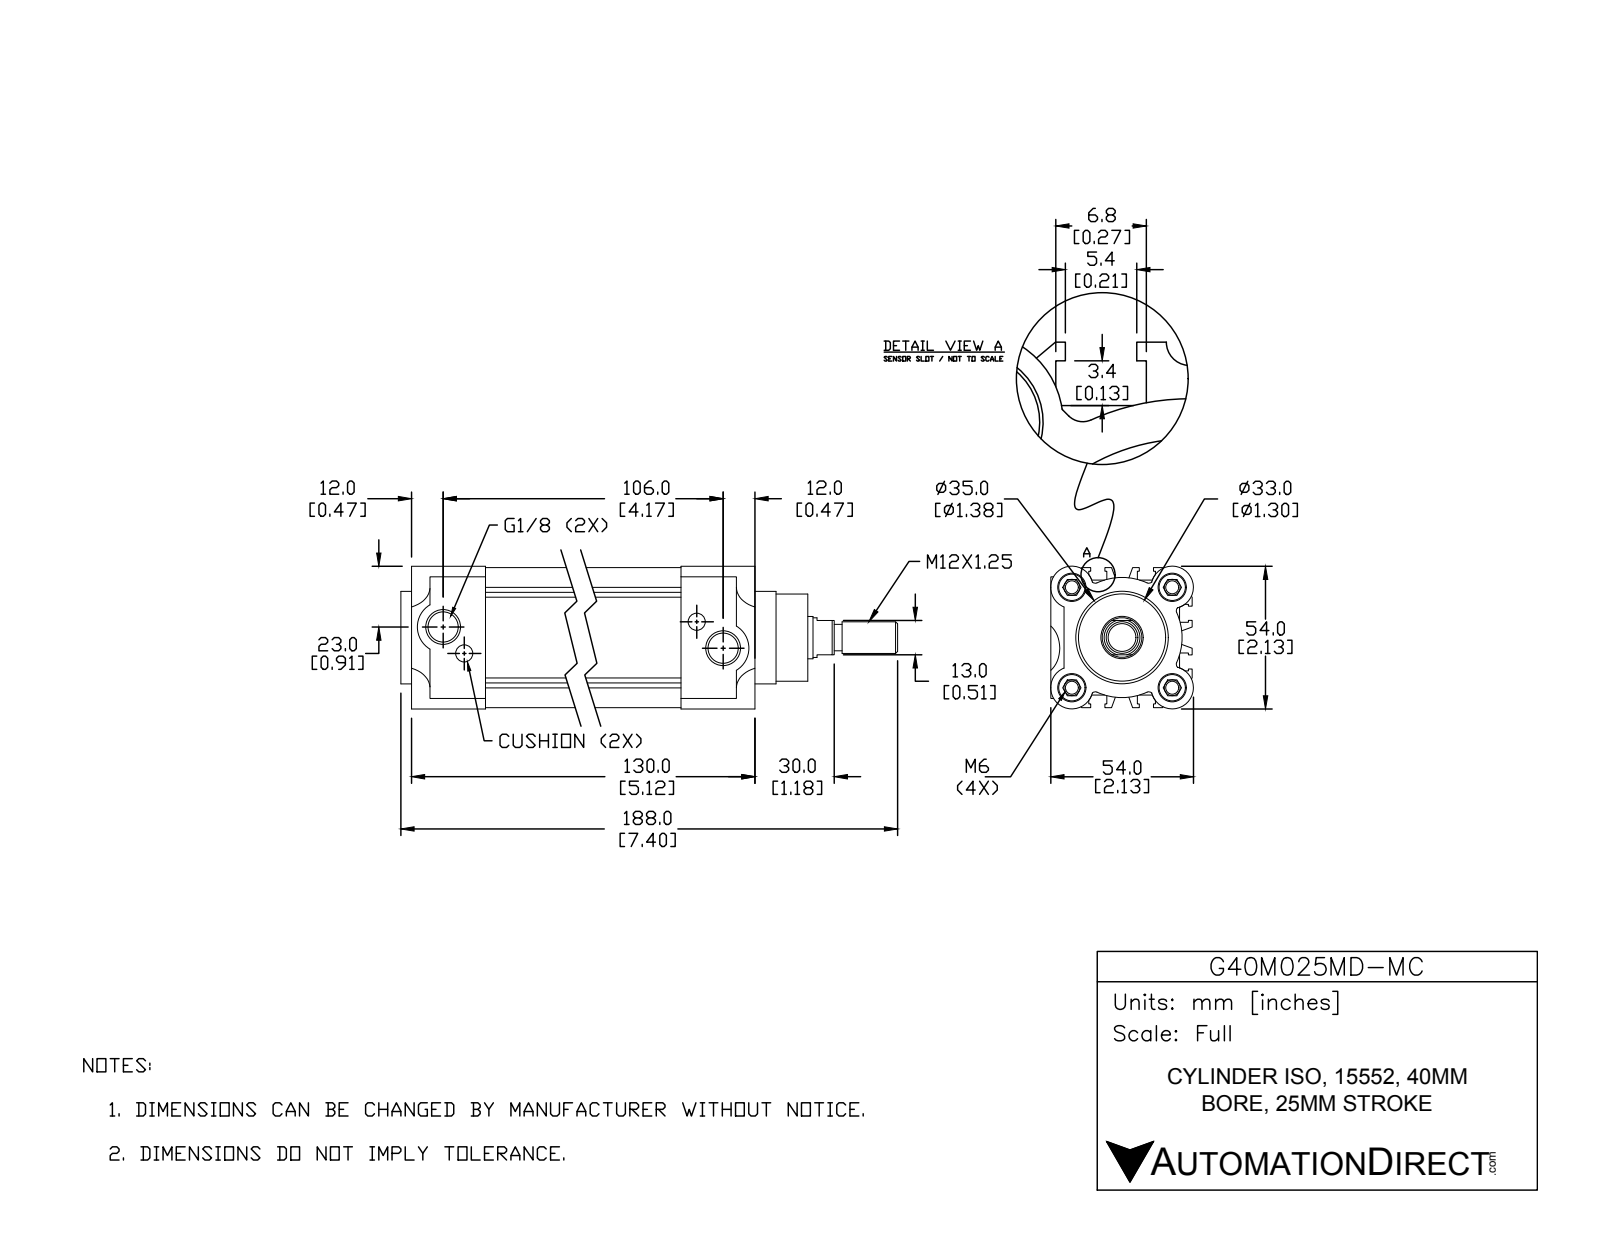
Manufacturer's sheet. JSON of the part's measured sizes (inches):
{"part_name": "40-HL; G40M025MD-MC; 40121-HR; 4012125-R (+1 more)", "step_written_by": "SolidWorks 2015 (CONFIG_CONTROL_DESIGN)", "units": "inches", "bodies": {"solids": 4, "faces": 418, "planar": 236, "cylindrical": 138, "other": 44}, "overall_size": [7.402, 2.126, 2.126], "volume_in3": 19, "surface_area_in2": 137, "round_holes": [[0.194, 4], [0.421, 4], [0.256, 2], [0.451, 2], [0.63, 1]], "round_bosses_or_shafts": [[0.394, 5], [1.575, 1], [1.378, 1], [1.299, 1], [0.591, 1], [0.472, 1]], "partial_cylinders_radius": [[0.059, 12], [0.004, 6], [0.295, 4], [0.315, 4], [0.384, 2], [0.886, 1], [0.896, 1]], "face_to_face_distances": [2.638, 0.276, 2.913, 1.378, 1.9, 0.187, 0.02, 1.26, 2.362, 1.102], "hole_center_spacings": [1.058, 1.496, 2.116, 0.504, 0.557, 3.496, 3.78, 3.859]}
